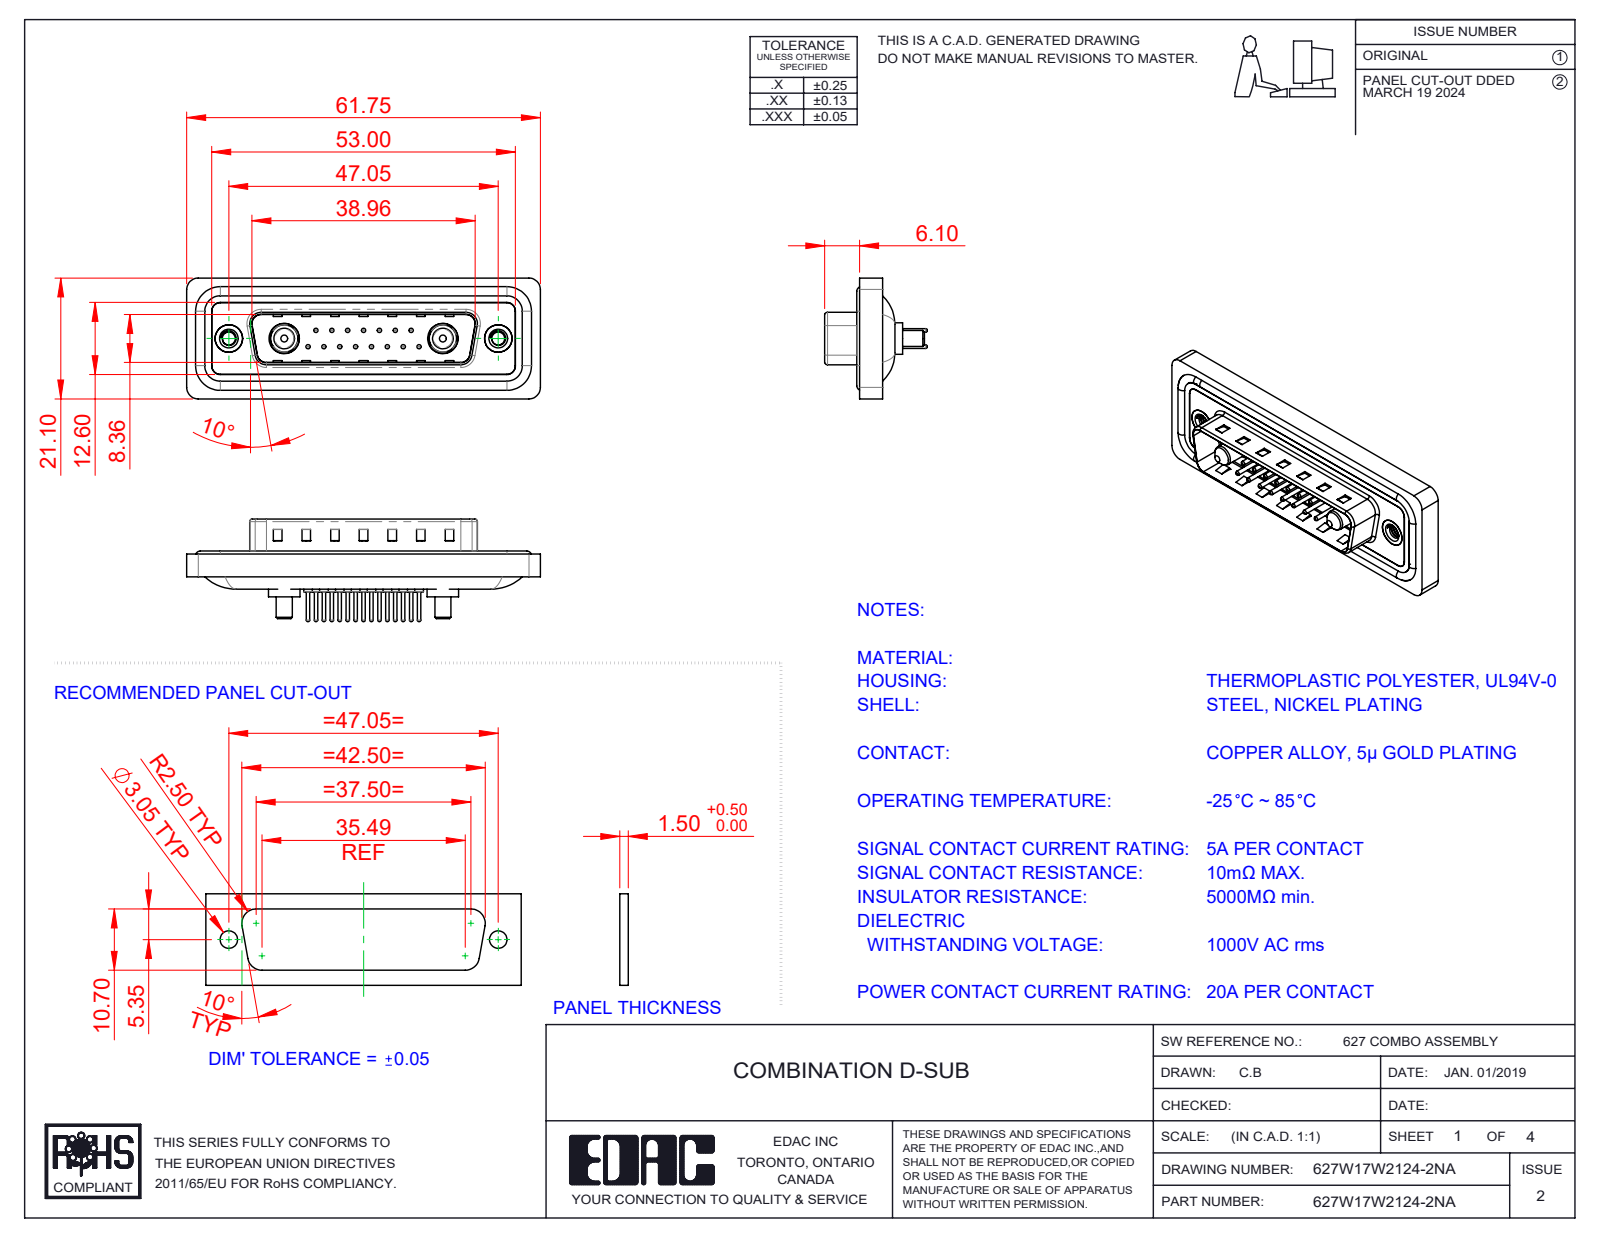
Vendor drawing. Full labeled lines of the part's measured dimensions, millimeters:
Part name (STEP PRODUCT): 627W17W2124-2NA; 627Combo Shell Front_25 Contacts; 627Combo Shell Rear_25 Contacts; 627Combo Housing_17W2 (+5 more)
STEP written by: SolidWorks 2023 (CONFIG_CONTROL_DESIGN)
Units: millimetres
Bodies: 26 solids, 1114 faces (334 planar, 438 cylindrical, 342 other)
Overall size (bounding box): 61.75 × 21.1 × 17.9
Volume: 7 268 mm³ · Surface area: 11 912 mm²
Round holes (diameter × count): ⌀0.75 ×15, ⌀1.6 ×15, ⌀2 ×15, ⌀2.26 ×2, ⌀4 ×2, ⌀4.8 ×2, ⌀4.85 ×2, ⌀5 ×2, ⌀5.3 ×2
Round bosses / shafts (diameter × count): ⌀1.5 ×15, ⌀0.6 ×15, ⌀1.6 ×4, ⌀5.5 ×2, ⌀5.2 ×2, ⌀4.9 ×2, ⌀4.75 ×2, ⌀3.75 ×2
Partial cylindrical surfaces — rounded edges, fillets, slot ends (radius × count): R1.5 ×22, R2 ×18, R0.5 ×8, R1.6 ×8, R0.25 ×4, R0.6 ×4, R0.65 ×4, R0.9 ×4
Main face-to-face distances: 0.4, 1.5, 1.1, 1.6, 0.5, 3.1, 2.9, 0.82, 9.58, 4.1
Hole centre spacings: 3.16, 2.77, 5.54, 8.31, 5.04, 7.49, 11.08, 5.03
